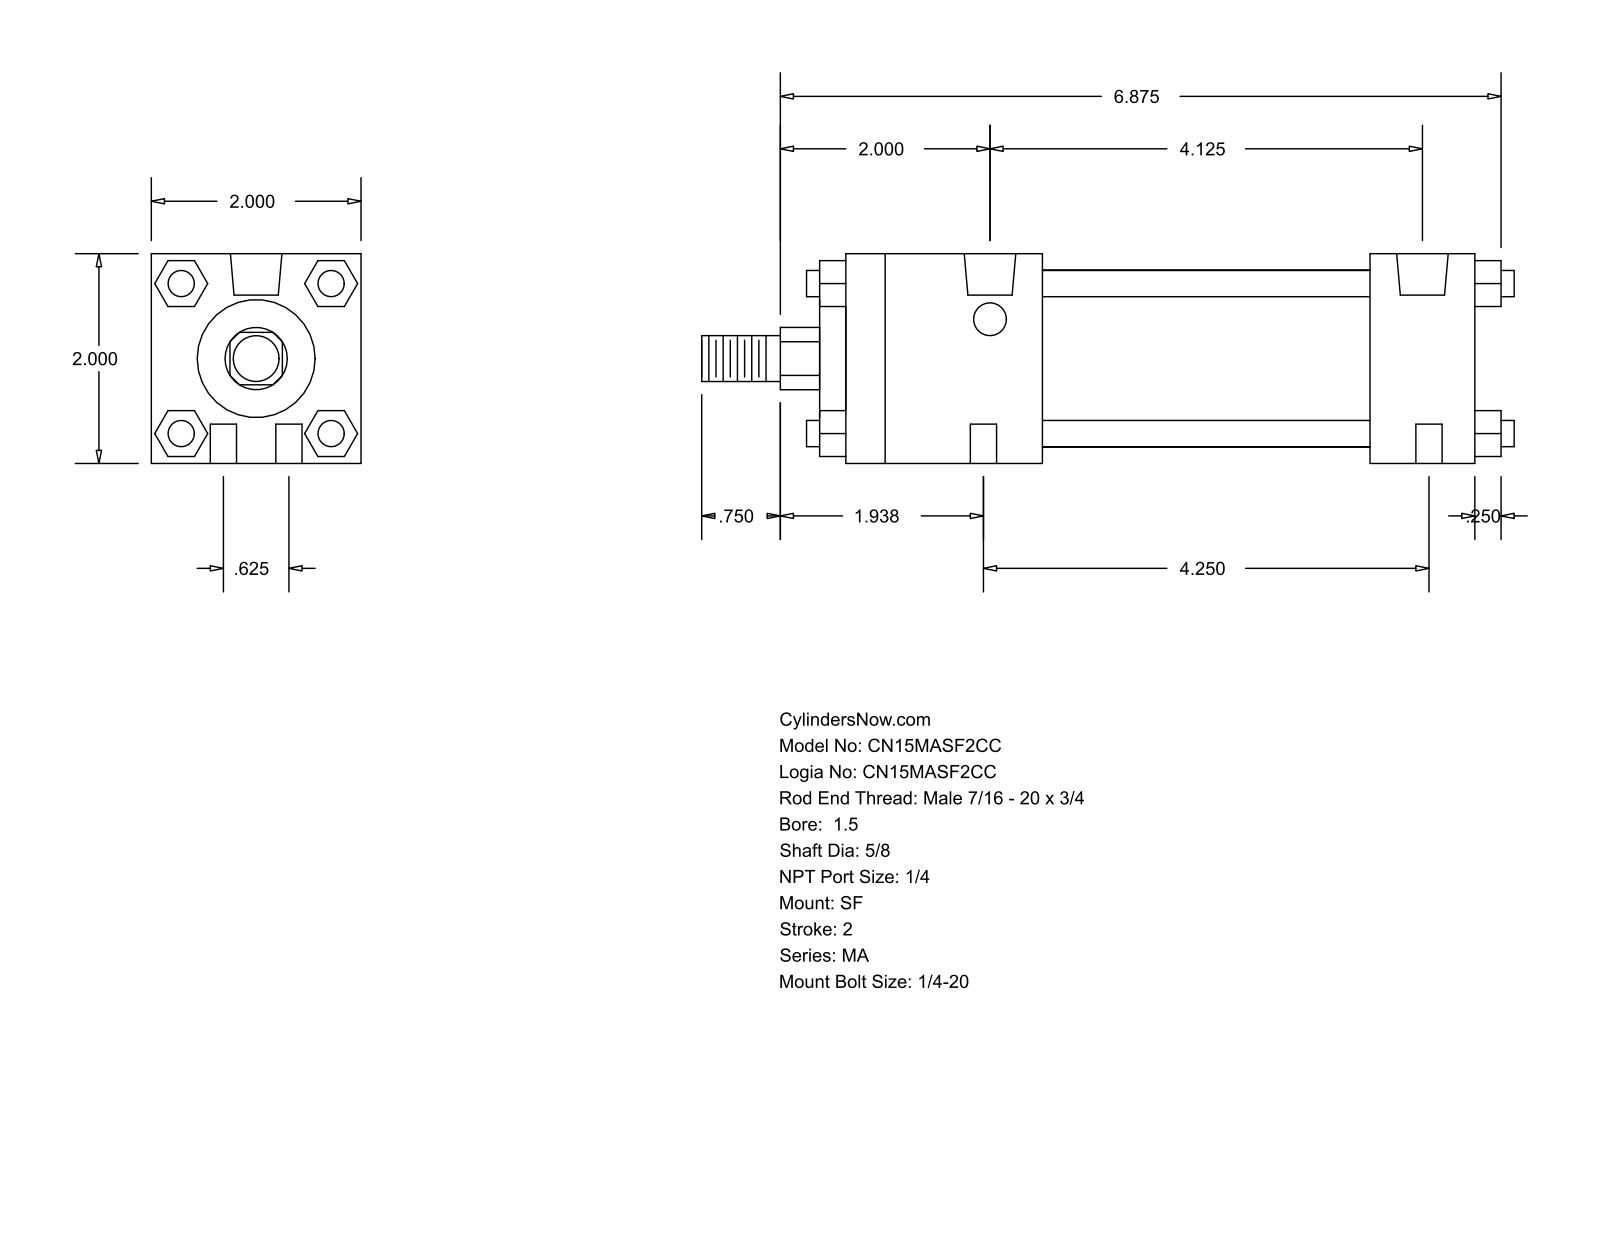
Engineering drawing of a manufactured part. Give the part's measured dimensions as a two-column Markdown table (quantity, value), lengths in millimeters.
| quantity | value |
| --- | --- |
| part name | MA_SF__0150_0.625 |
| STEP written by | GSSL Pune (CONFIG_CONTROL_DESIGN) |
| units | millimeters |
| bodies | 0 solids, 124 faces (94 planar, 30 cylindrical, 0 other) |
| overall size | 196.85 × 50.8 × 50.8 |
| round holes (diameter × count) | 6.35 × 4, 7.94 × 2, 12.49 × 2 |
| round bosses / shafts (diameter × count) | 6.35 × 4, 42.93 × 1, 28.57 × 1, 15.88 × 1, 11.11 × 1 |
| partial cylindrical surfaces (radius × count) | 7.54 × 1 |
| main face-to-face distances | 50.8, 152.4, 25.4, 47.62, 127, 79.38, 104.78, 6.35, 53.97, 133.35 |
| hole center spacings | 8.1, 106.66, 15.88, 104.77, 107.95, 109.11 |
